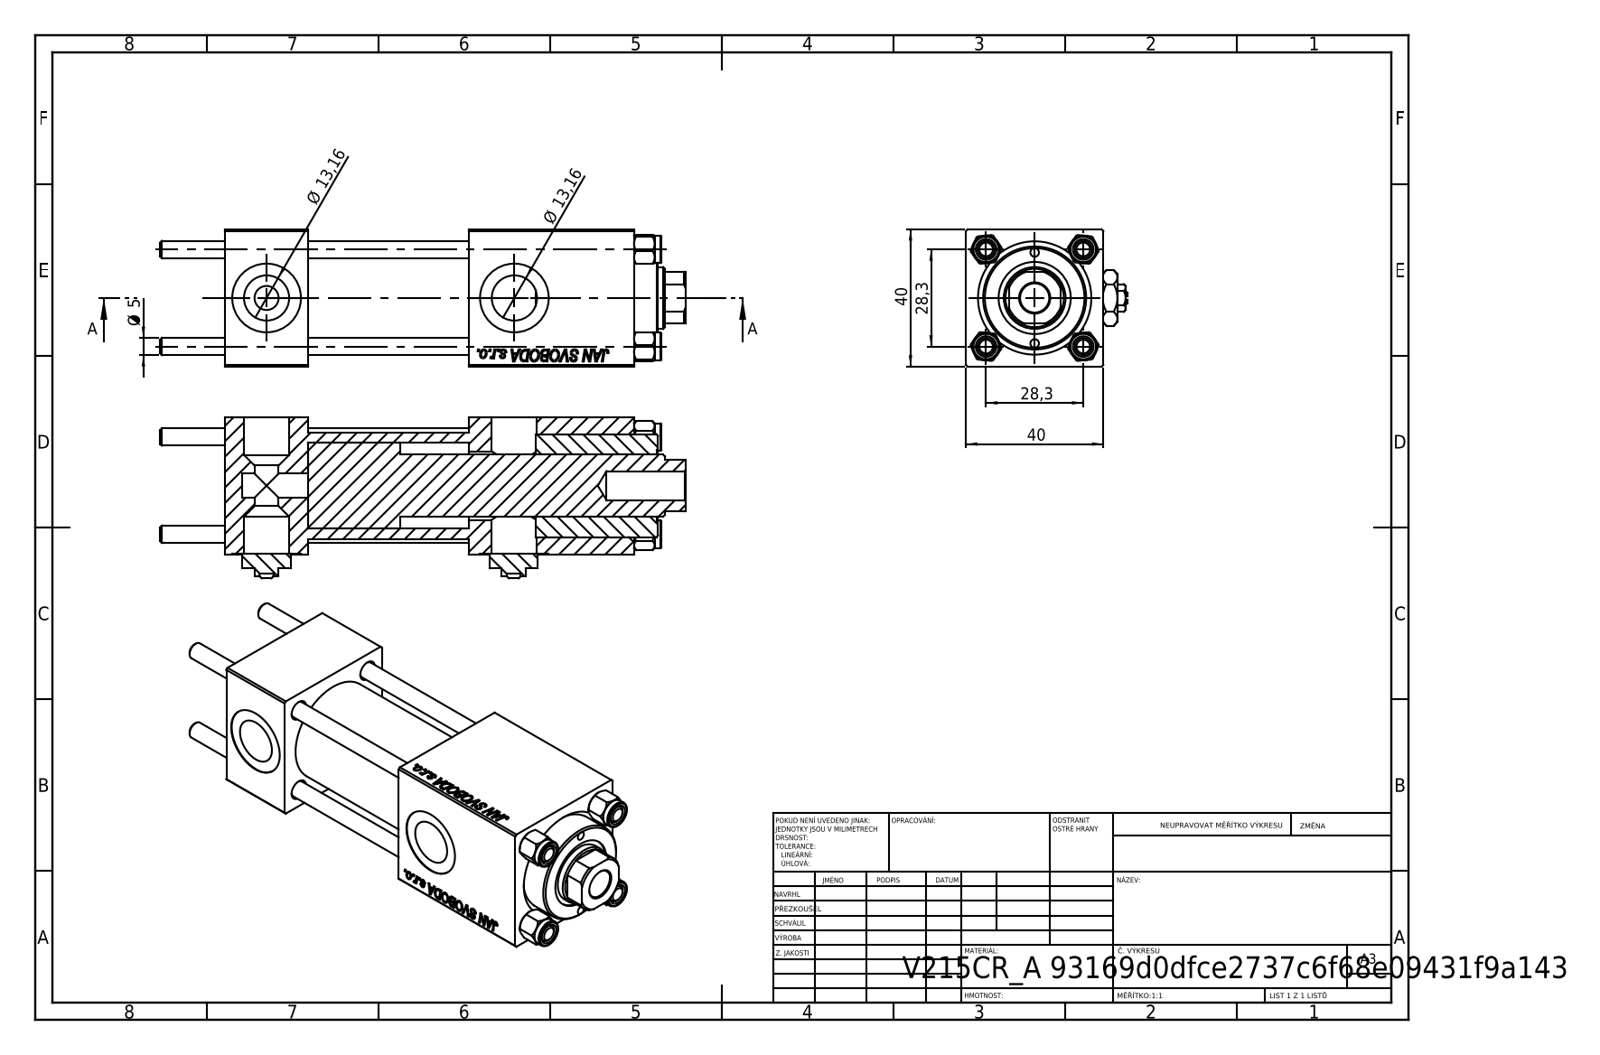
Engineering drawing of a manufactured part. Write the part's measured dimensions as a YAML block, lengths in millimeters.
part_name: "CR025_012_A_0_G_A_G_M_020_+#_##_TYCINKA; V215CR_VCP; Zatka_pro_OIL_PORT; V215_VC_A (+2 more)"
step_written_by: "SolidWorks 2019 (CONFIG_CONTROL_DESIGN)"
units: millimeters
bodies: {solids: 13, faces: 1235, planar: 565, cylindrical: 92, other: 578}
overall_size: [153, 47, 40]
volume: 150546
surface_area: 63154
round_holes:
  - {diameter: 5, count: 4}
  - {diameter: 20, count: 4}
  - {diameter: 13.16, count: 3}
  - {diameter: 2.5, count: 2}
  - {diameter: 7, count: 2}
  - {diameter: 8.5, count: 1}
  - {diameter: 13, count: 1}
  - {diameter: 18, count: 1}
  - {diameter: 21, count: 1}
  - {diameter: 25, count: 1}
  - {diameter: 30, count: 1}
round_bosses_or_shafts:
  - {diameter: 8, count: 4}
  - {diameter: 31, count: 1}
partial_cylinders:
  - {radius: 8.5, count: 1}
face_to_face_distances: [40, 24, 39.8, 47, 71, 90.3, 66.3, 19.3, 95, 119]
hole_center_spacings: [14.18, 20.01, 28.3, 30.84, 13.25, 40.02, 26.5, 72]
